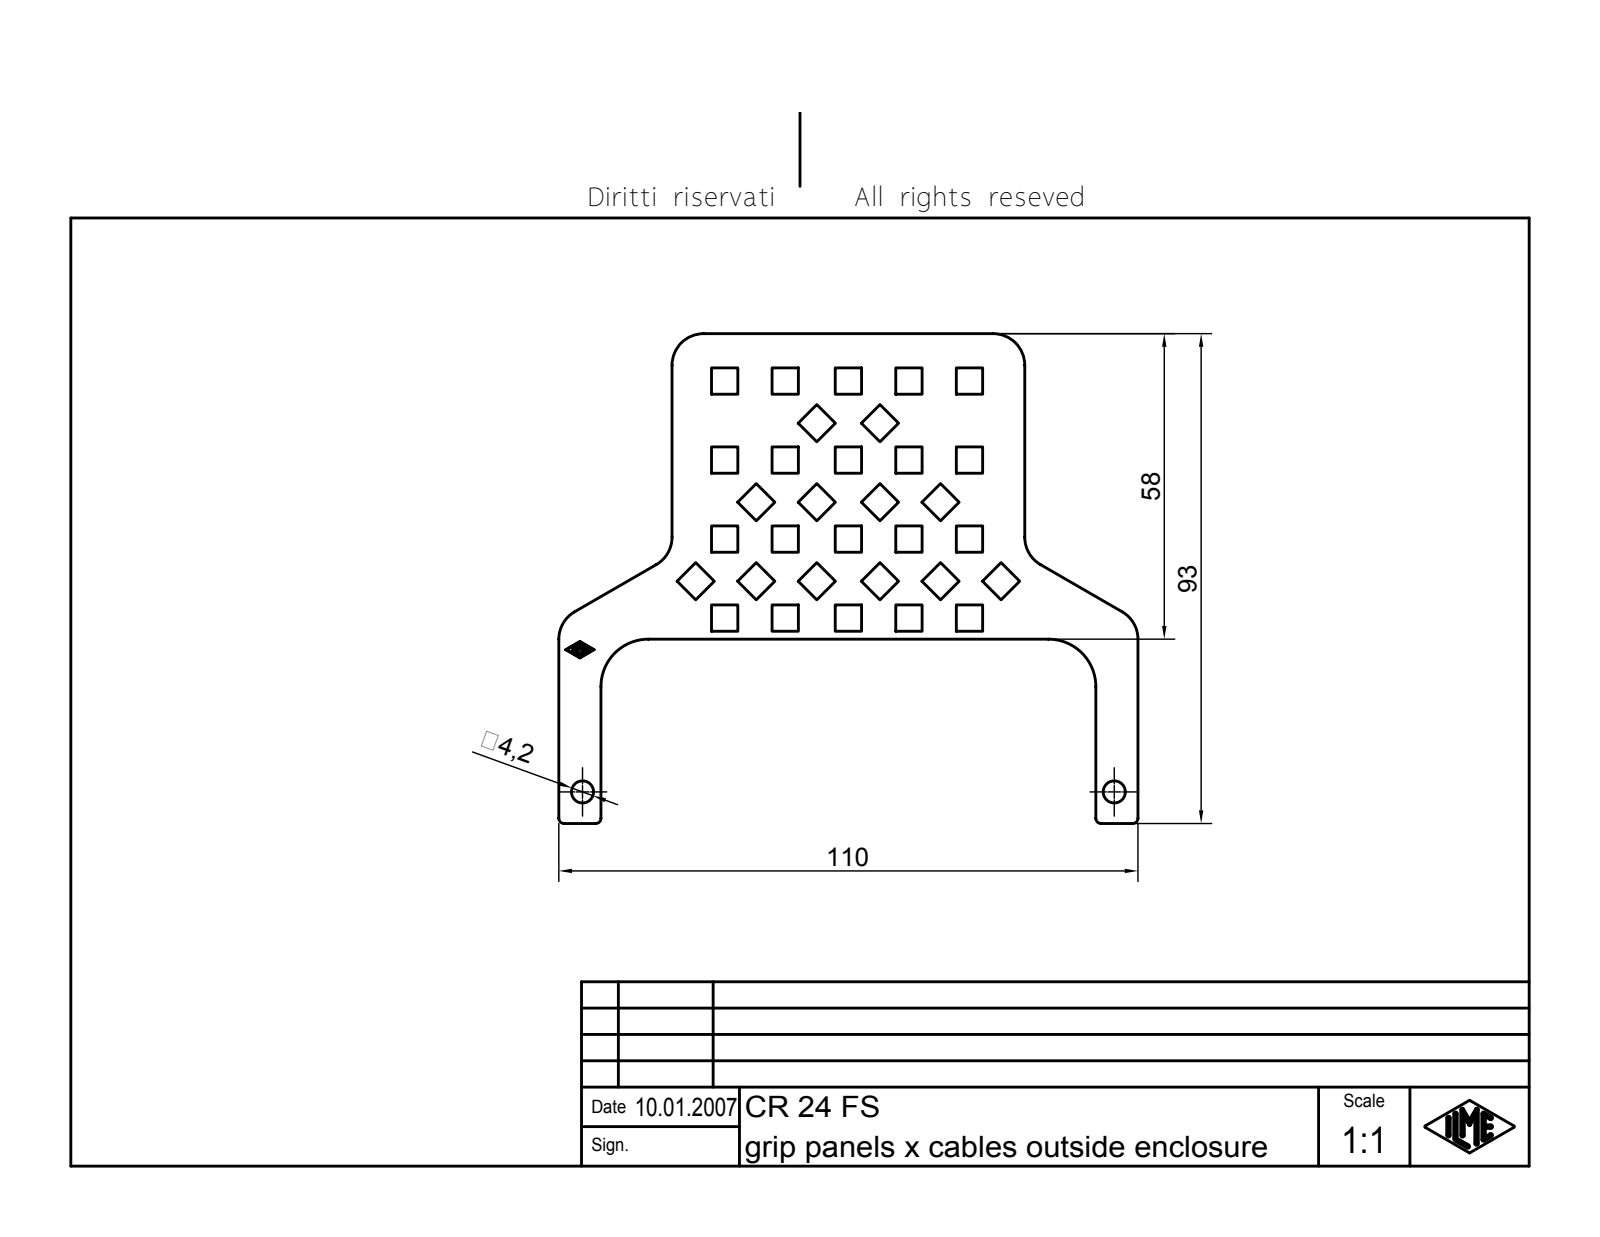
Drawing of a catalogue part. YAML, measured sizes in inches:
part_name: "CR 24 FS"
step_written_by: "Autodesk Inventor 7 (AUTOMOTIVE_DESIGN)"
units: inches
bodies: {solids: 1, faces: 213, planar: 179, cylindrical: 34, other: 0}
overall_size: [4.331, 3.661, 0.079]
volume: 0.495
surface_area: 16.01
round_holes:
  - {diameter: 0.165, count: 2}
partial_cylinders:
  - {radius: 0.004, count: 14}
  - {radius: 0.236, count: 6}
  - {radius: 0.039, count: 4}
  - {radius: 0.354, count: 2}
face_to_face_distances: [0.079, 0.197, 0.591, 0.453, 1.378, 1.181, 0.846, 0.256, 0.65, 2.028]
hole_center_spacings: [3.976]
